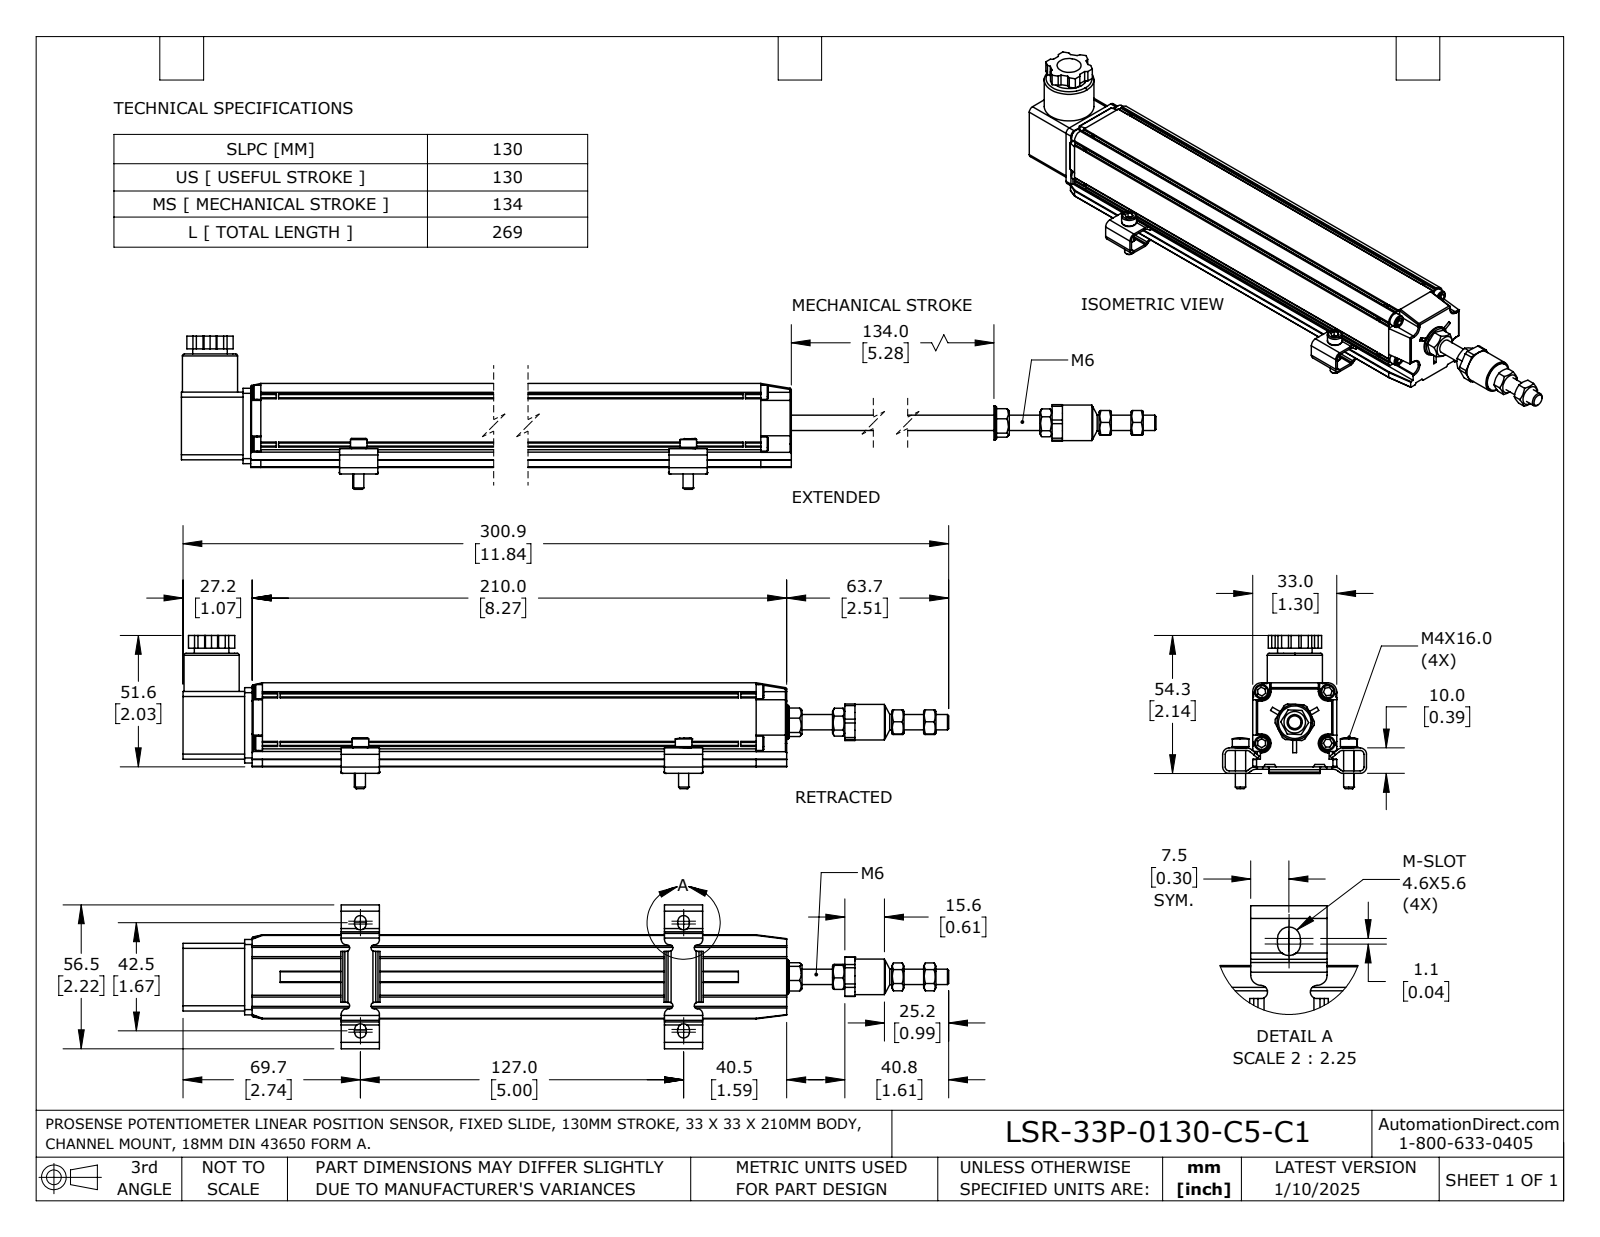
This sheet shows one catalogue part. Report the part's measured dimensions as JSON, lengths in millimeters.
{"part_name": "LSR-33P-0130-C5-C1", "step_written_by": "SolidWorks 2023 (AUTOMOTIVE_DESIGN)", "units": "millimeters", "bodies": {"solids": 14, "faces": 901, "planar": 579, "cylindrical": 253, "other": 69}, "overall_size": [300.8, 60.2, 56.5], "volume_mm3": 226000, "surface_area_mm2": 69810, "round_holes": [[2.7, 4], [3.3, 4], [4.3, 1], [5.2, 1], [5.3, 1], [5.9, 1], [7, 1], [7.2, 1], [10, 1], [10.5, 1], [14.6, 1], [15.3, 1]], "round_bosses_or_shafts": [[4, 5], [3, 5], [6.5, 4], [5.6, 4], [21.7, 1], [14, 1], [13.6, 1], [13.4, 1]], "partial_cylinders_radius": [[2, 28], [0.5, 23], [0.2, 16], [1.3, 8], [1.5, 8], [2.3, 8], [3, 8], [1, 4]], "face_to_face_distances": [33, 3, 1, 5.6, 30, 2.6, 1.6, 2, 27.4, 3.6], "hole_center_spacings": [1.2, 14.8, 15.4, 17.7, 18.5, 20.3, 26, 33]}
